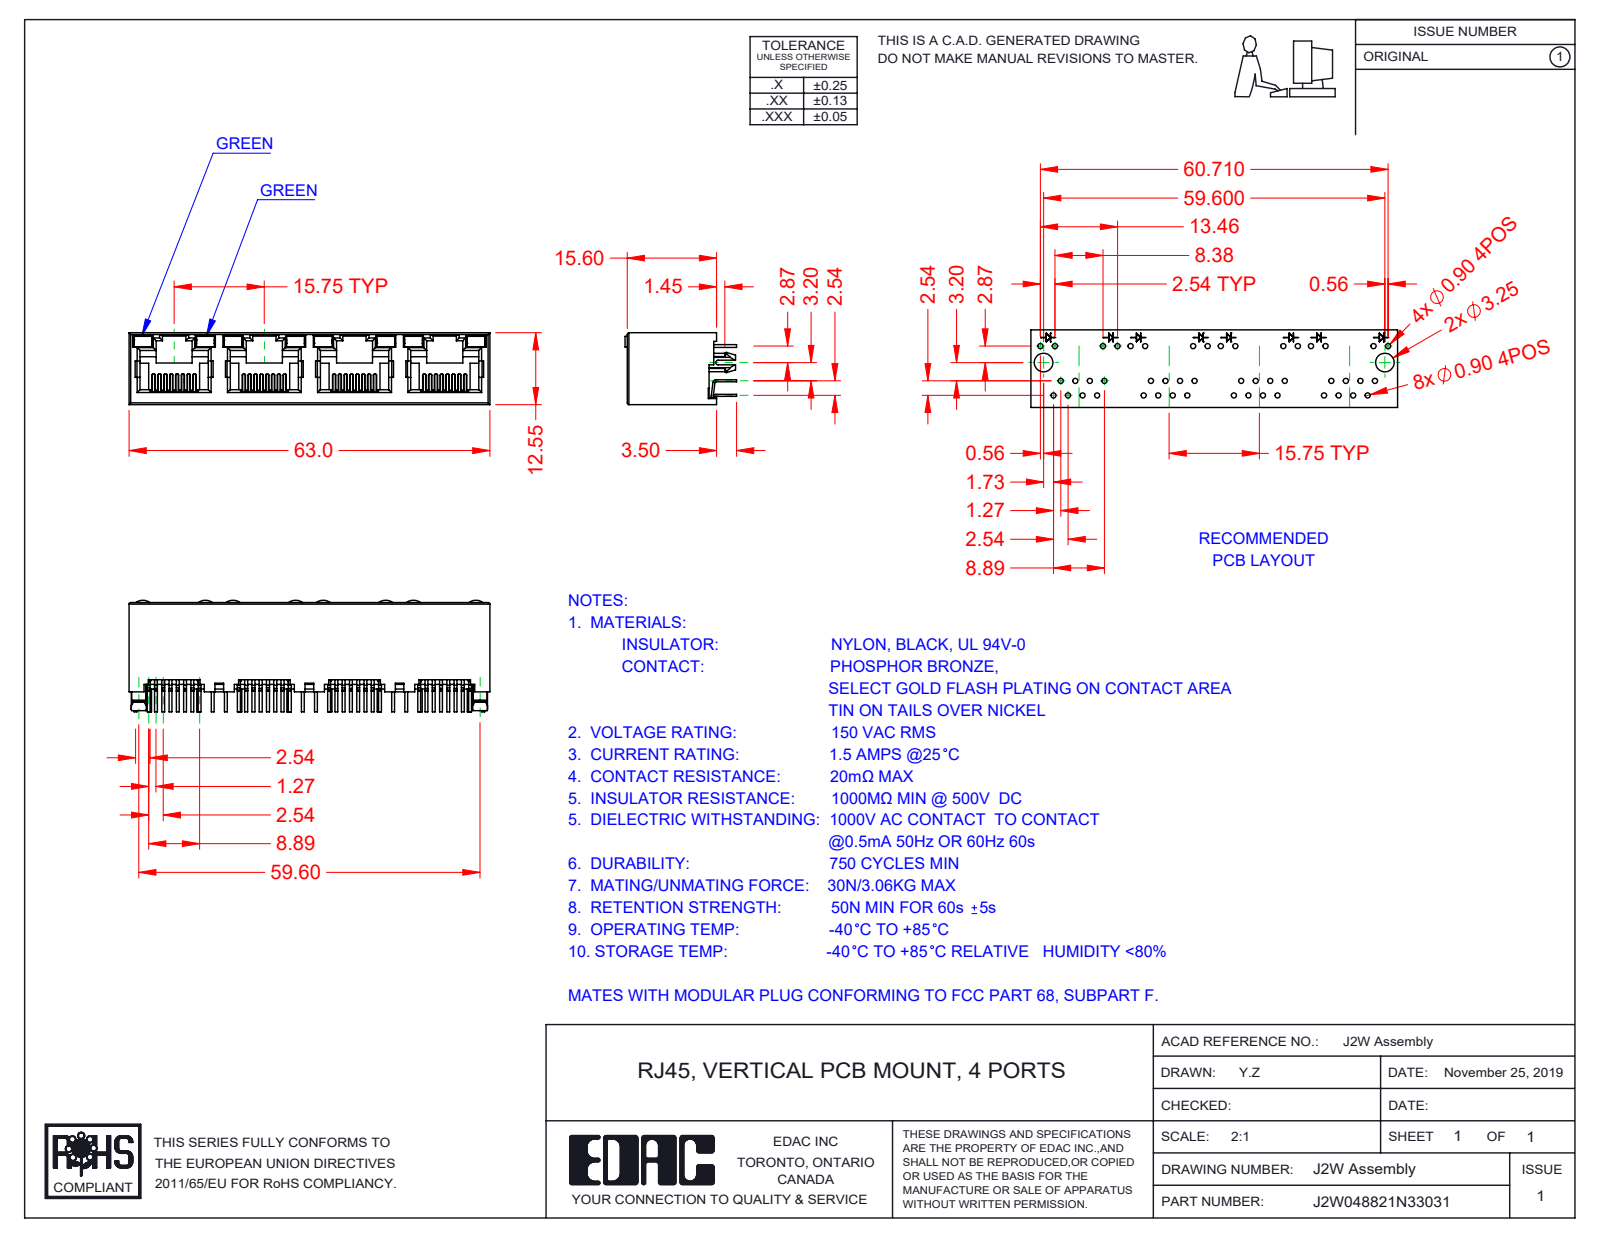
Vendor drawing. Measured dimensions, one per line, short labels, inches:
name: 2W LED RH_3-Green; 2W LED LH_3-Green; 2W Insulator; 2W Contacts (+2 more)
written by: SolidWorks 2020 (CONFIG_CONTROL_DESIGN)
unit: in
bodies: 45 solids, 3135 faces (2600 planar, 477 cylindrical, 58 other)
size: 2.48 × 0.768 × 0.494
volume: 0.326 in³; area: 20.37 in²
rounds: 64× R0.006, 29× R0.008, 28× R0.02, 14× R0.012, 8× R0.018, 8× R0.079, 2× R0.01, 2× R0.059
face distances: 0.494, 0.469, 0.026, 0.62, 0.014, 0.059, 0.031, 0.024, 0.445, 1.24
